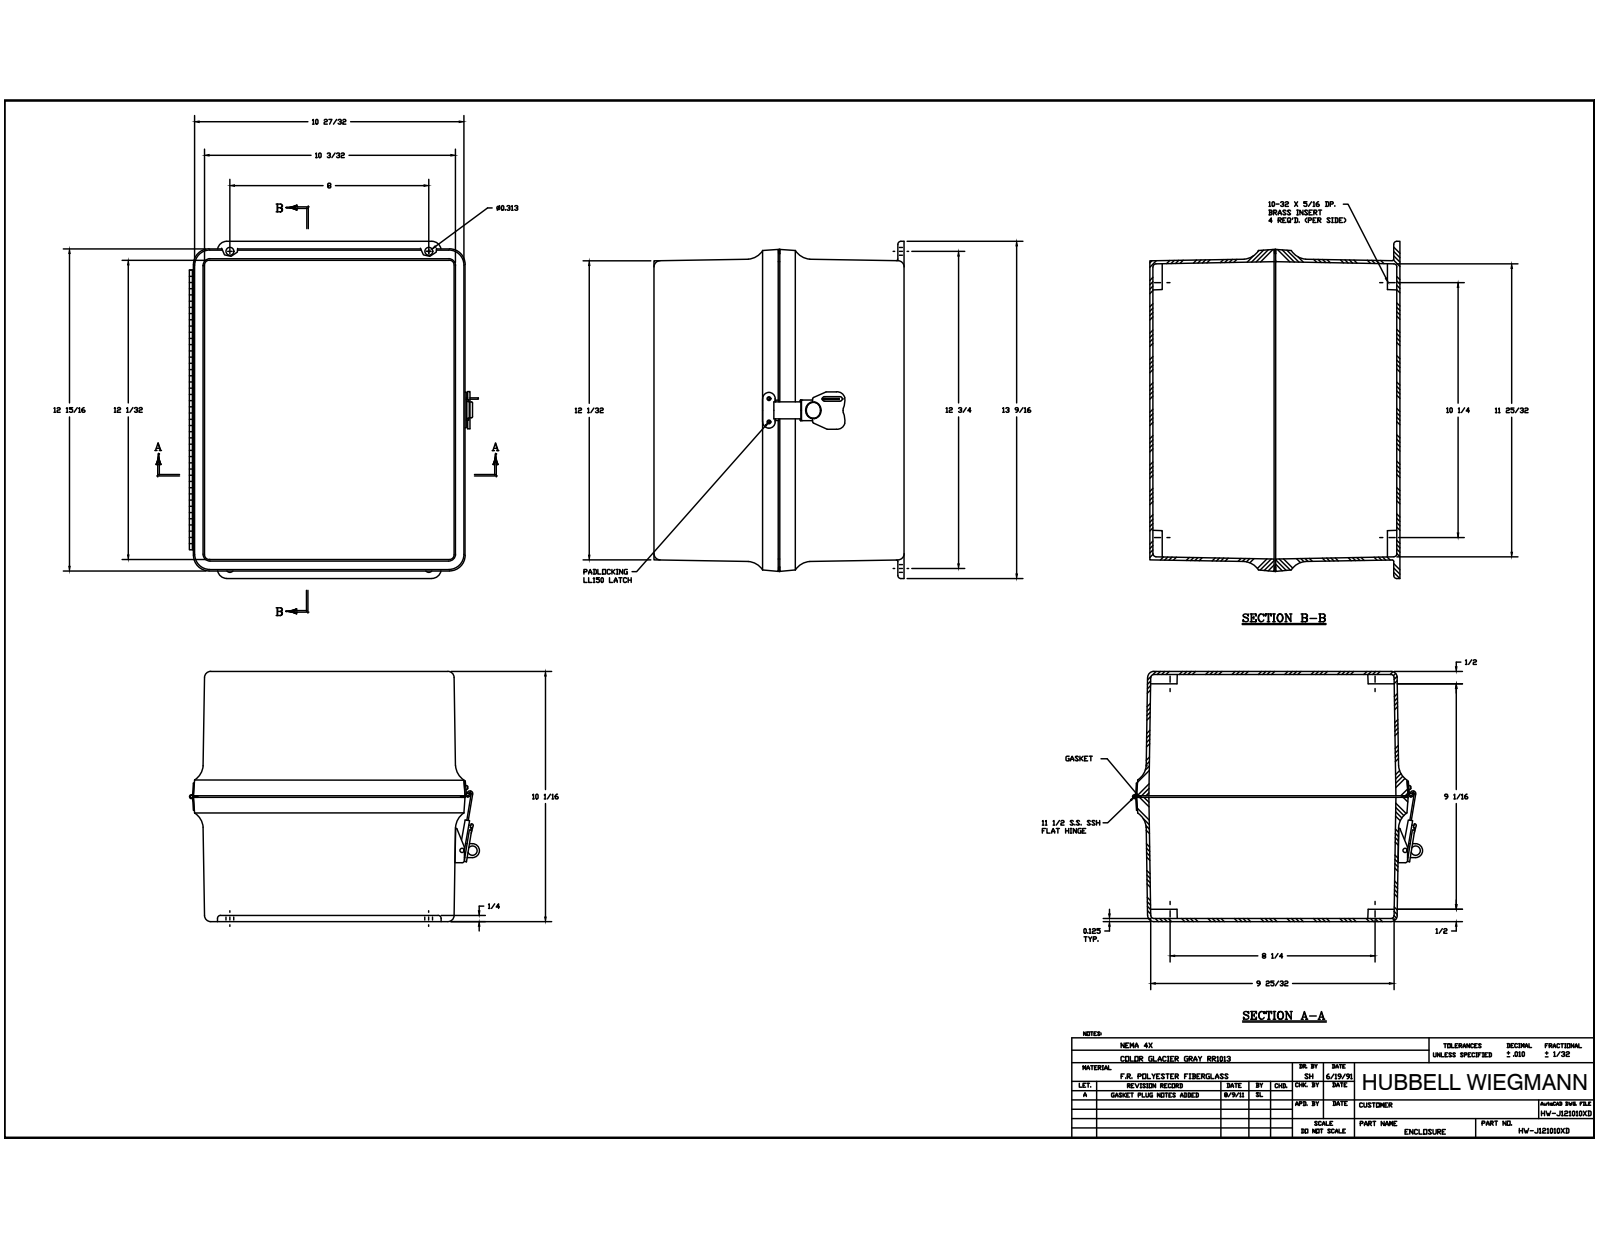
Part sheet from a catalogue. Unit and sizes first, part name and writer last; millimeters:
Units: millimetres
Overall size (bounding box): 344.49 × 295.14 × 255.23
Round holes (diameter × count): ⌀3.56 ×12, ⌀3.86 ×11, ⌀3.45 ×8, ⌀3.96 ×6, ⌀5.54 ×4, ⌀3.3 ×2, ⌀4.2 ×2, ⌀5 ×2, ⌀2.16 ×1, ⌀2.7 ×1, ⌀3 ×1, ⌀3.5 ×1
Round bosses / shafts (diameter × count): ⌀6.35 ×12, ⌀3.17 ×12, ⌀6.86 ×6, ⌀14.8 ×1, ⌀13.3 ×1, ⌀5.3 ×1, ⌀4.7 ×1, ⌀3.94 ×1
Partial cylindrical surfaces — rounded edges, fillets, slot ends (radius × count): R0.79 ×88, R19.05 ×13, R3.17 ×12, R6.35 ×12, R2 ×10, R0.95 ×4, R1 ×4, R1.15 ×4
Main face-to-face distances: 3.17, 248.88, 255.23, 252.43, 3.18, 252.06, 252.05, 303.79, 258.98, 310.34
Hole centre spacings: 92.08, 174.62, 235, 285.58, 17.08, 34.24, 266.7, 368.25
Volume: 1 882 000 mm³ · Surface area: 967 139 mm²
Bodies: 37 solids, 1229 faces (455 planar, 472 cylindrical, 302 other)
Part name (STEP PRODUCT): J1210SSH; RMINS45821P_113; RMINS45821P_114; RMINS45821P_115 (+8 more)
STEP written by: Autodesk Inventor 2014 (AUTOMOTIVE_DESIGN)
